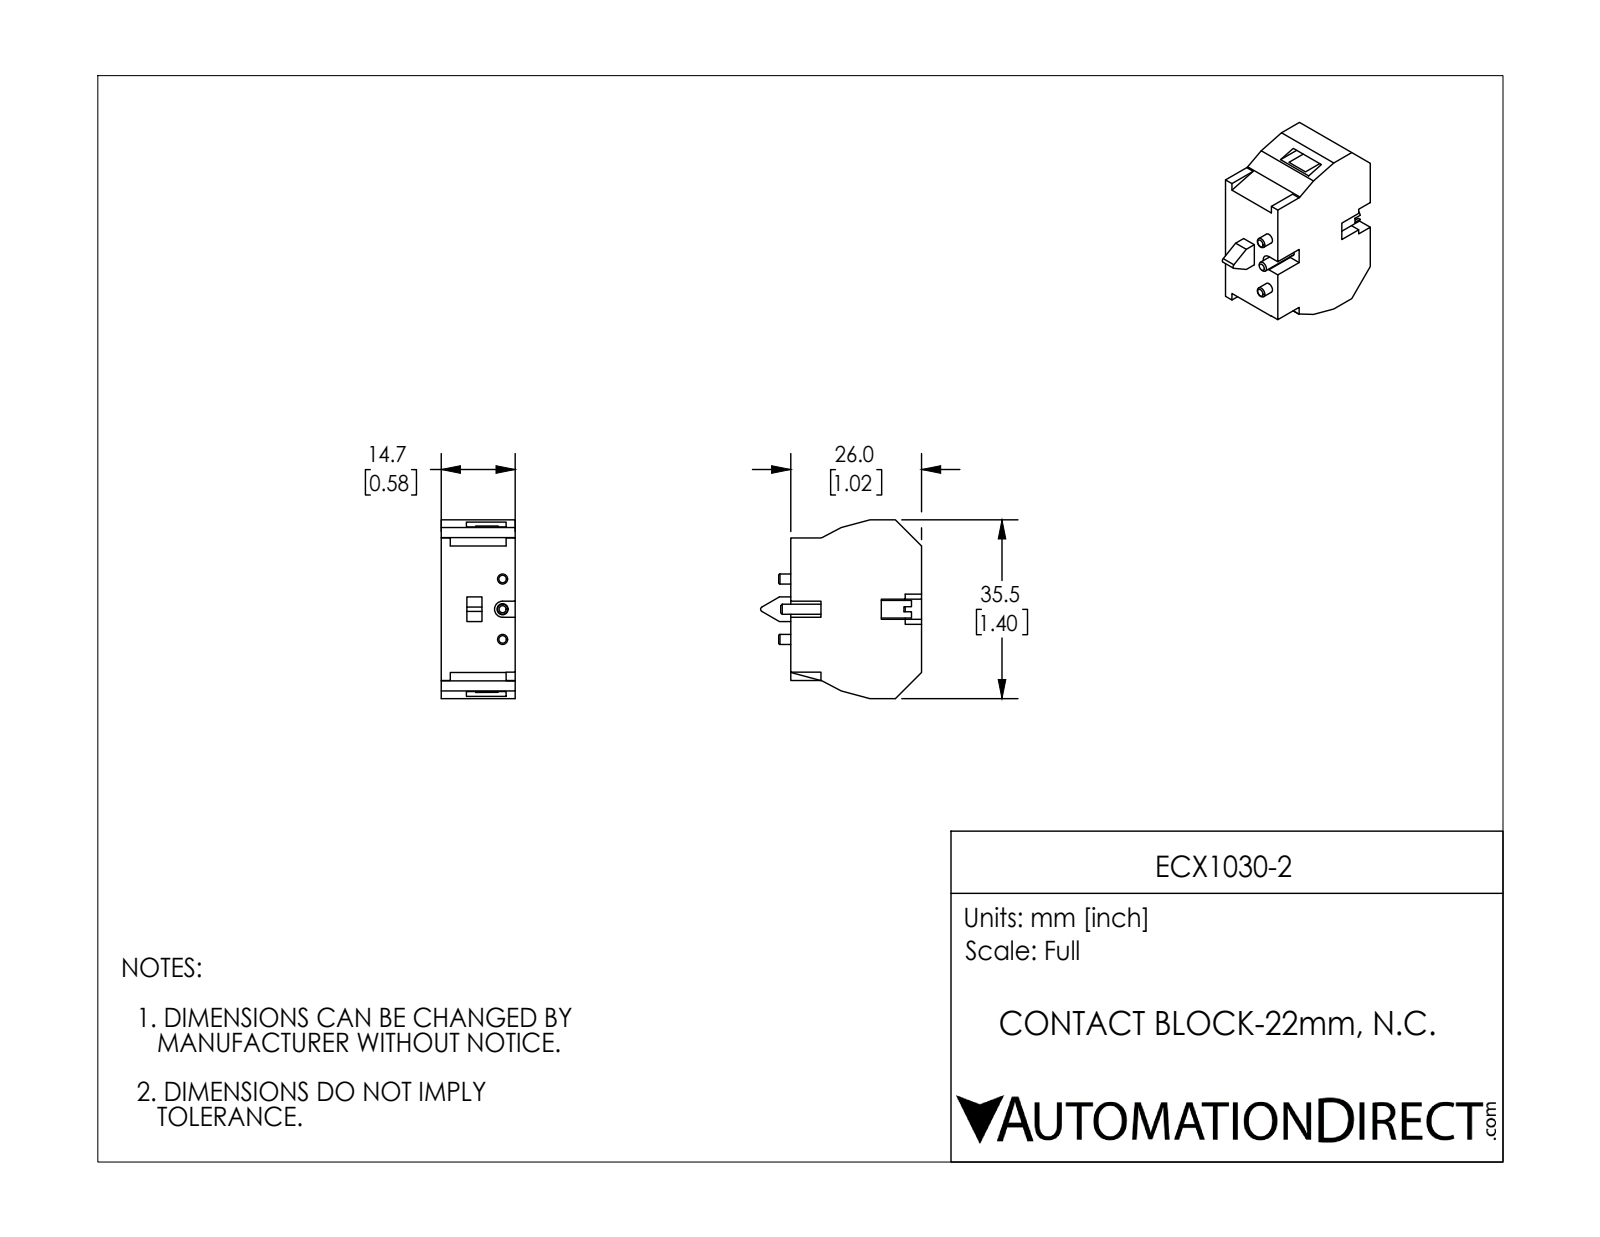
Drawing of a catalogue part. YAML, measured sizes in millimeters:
part_name: "ECX1030-2"
step_written_by: "SolidWorks 2016 (AUTOMOTIVE_DESIGN)"
units: millimeters
bodies: {solids: 1, faces: 93, planar: 75, cylindrical: 14, other: 4}
overall_size: [35.54, 32, 14.7]
volume: 10661
surface_area: 4346
round_holes:
  - {diameter: 2, count: 2}
  - {diameter: 2.2, count: 1}
partial_cylinders:
  - {radius: 0.5, count: 1}
  - {radius: 1.6, count: 1}
  - {radius: 2, count: 1}
face_to_face_distances: [14.7, 26, 6.84, 7.86, 0.45, 12.9, 6.87, 28.67, 0.95, 35.09]
hole_center_spacings: [6, 12]
